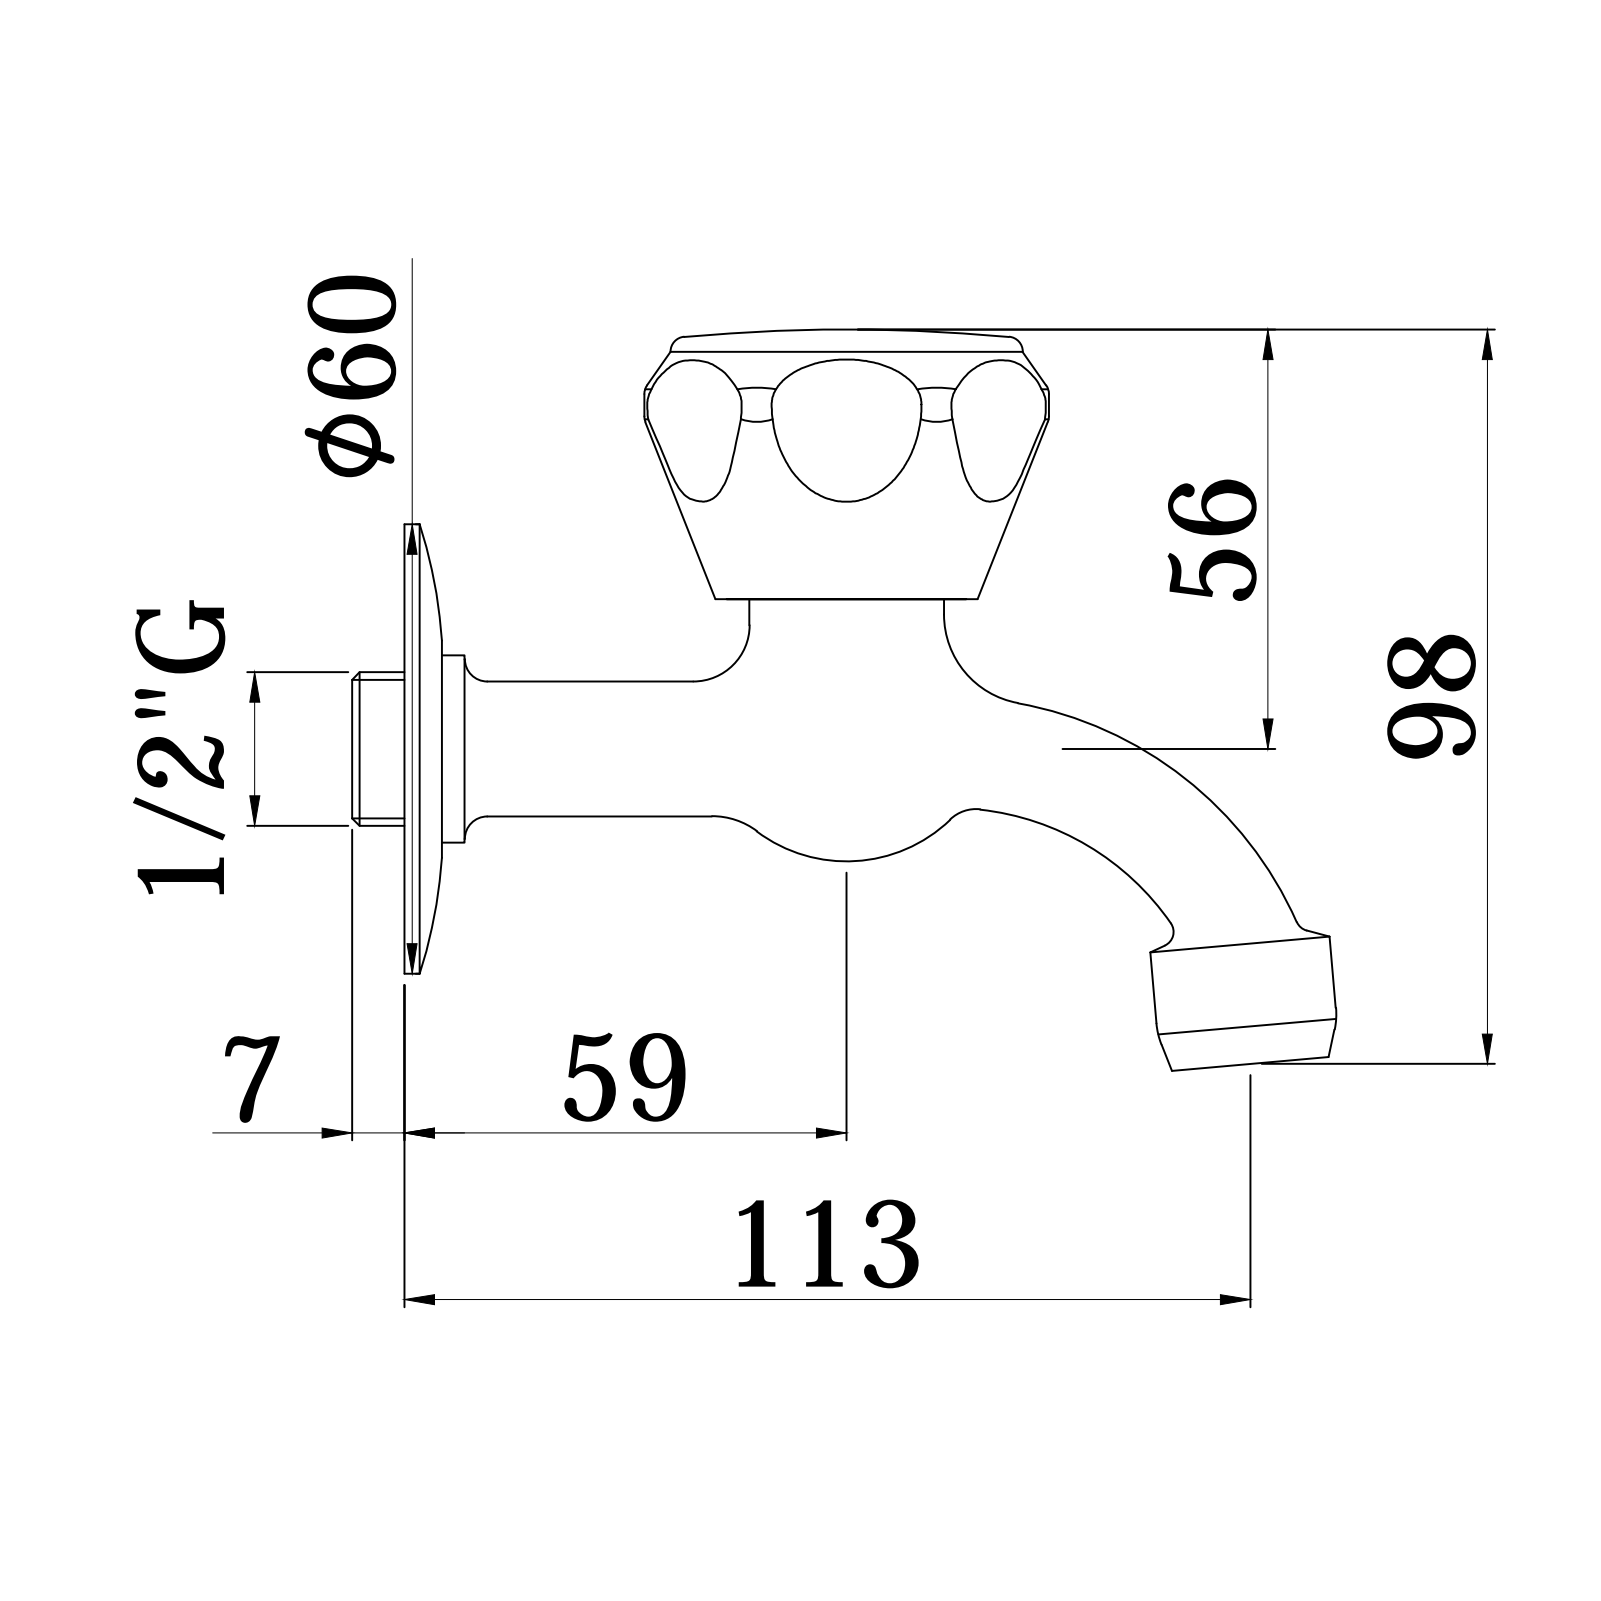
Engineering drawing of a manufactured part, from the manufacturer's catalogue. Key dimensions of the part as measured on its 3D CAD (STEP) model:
Part name (STEP PRODUCT): DA213CR
STEP written by: CREO PARAMETRIC BY PTC INC, 2020044 (CONFIG_CONTROL_DESIGN)
Units: millimetres
Bodies: 1 solid, 141 faces (8 planar, 22 cylindrical, 111 other)
Overall size (bounding box): 126.8 × 101.75 × 58
Volume: 134 644 mm³ · Surface area: 23 889 mm²
Round bosses / shafts (diameter × count): ⌀58 ×1, ⌀38.5 ×1, ⌀26.5 ×1, ⌀24.7 ×1, ⌀23.6 ×1, ⌀22 ×1, ⌀21 ×1
Partial cylindrical surfaces — rounded edges, fillets, slot ends (radius × count): R21.31 ×8
Main face-to-face distances: 63.05, 98.35, 35.3, 7.7, 98.75, 35.7, 0.4, 13, 5.3, 15.9
